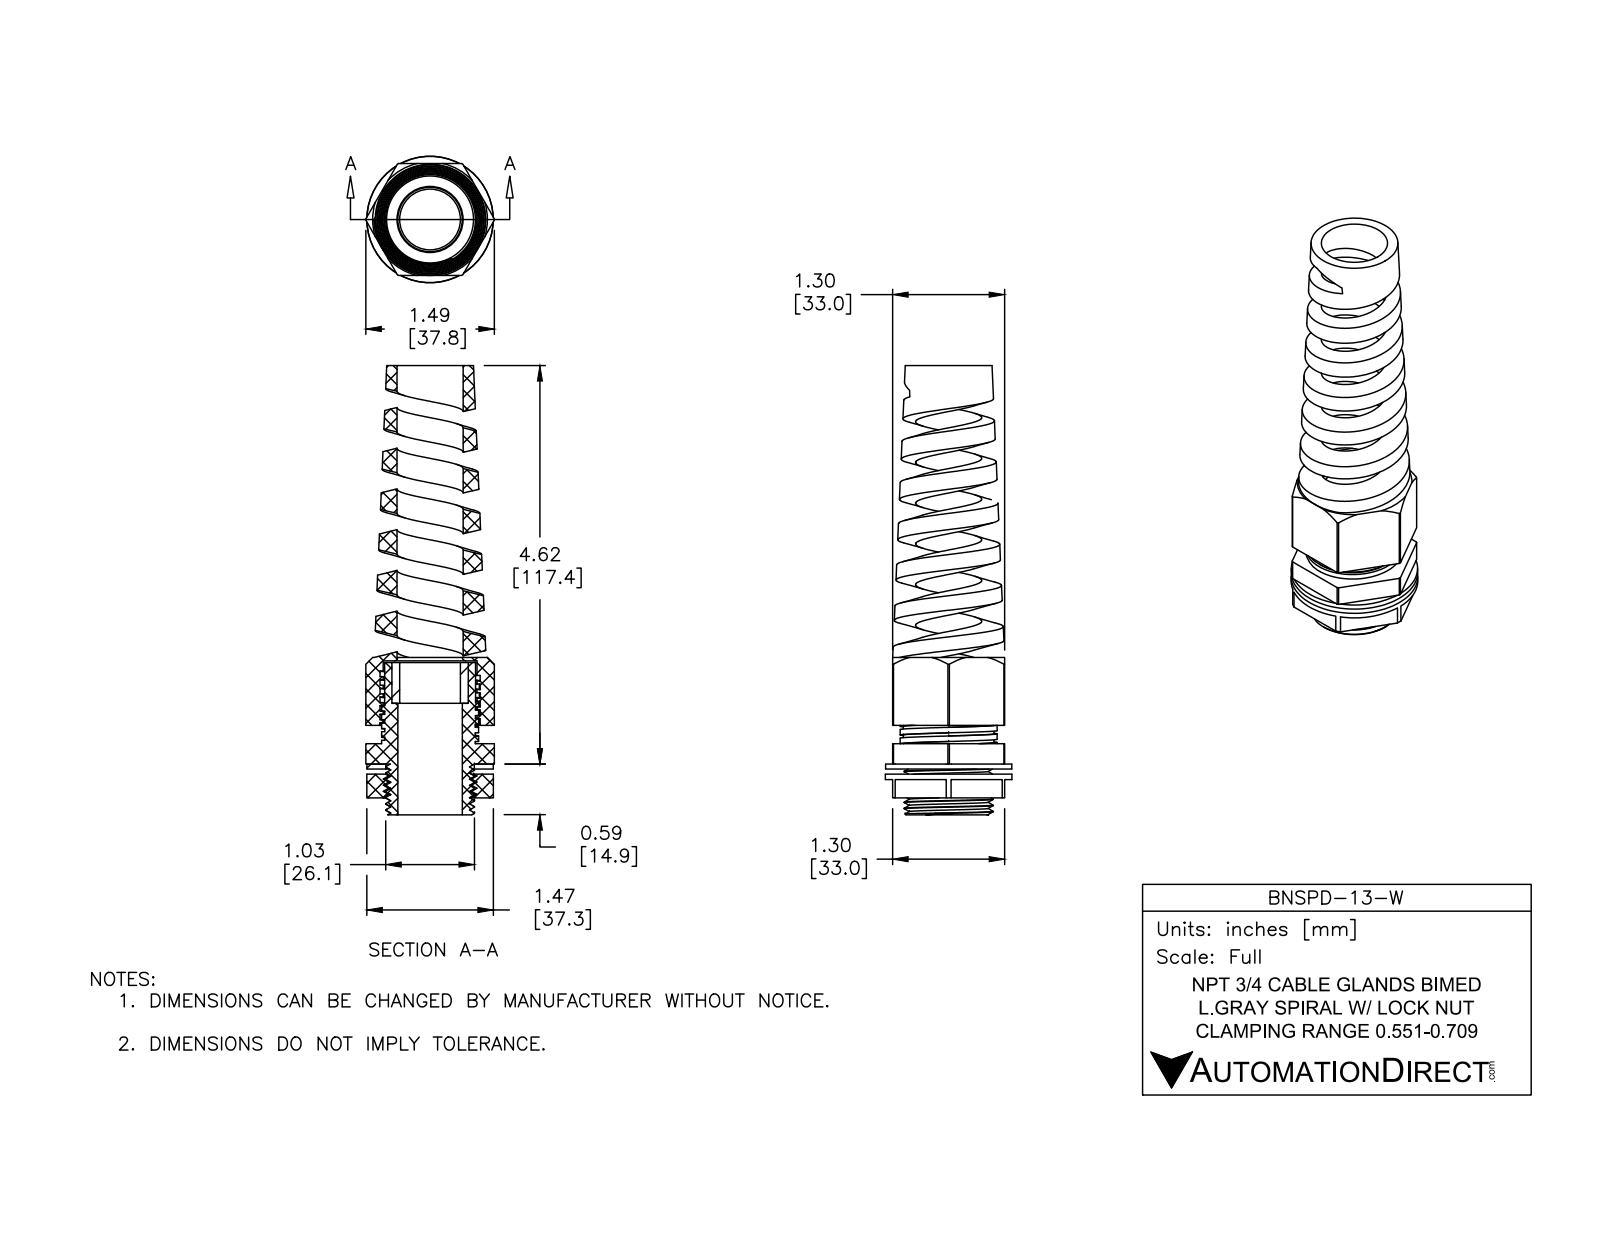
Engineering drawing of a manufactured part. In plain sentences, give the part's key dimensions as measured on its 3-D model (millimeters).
The part is named "BNSPDX-13-W". Its 3-D file was written by "SolidWorks 2015 (CONFIG_CONTROL_DESIGN)". It is 5 solids with 238 faces: 105 planar, 96 cylindrical and 37 other. Overall it measures 132.38 by 37.85 by 37.3 millimeters. Its volume is 41 282 cubic millimeters and its surface area 35 007 square millimeters. Round holes: 1 of diameter 17.9, 1 of diameter 19, 1 of diameter 19.5, 1 of diameter 22.5, 1 of diameter 24.69, 1 of diameter 26.1, 1 of diameter 27.67. Round bosses or shafts: 1 of diameter 37.3, 1 of diameter 37.2, 1 of diameter 28.6, 1 of diameter 26.8, 1 of diameter 26.14. Partial cylindrical surfaces (rounded edges, fillets, slot ends): 1 of radius 18.92. The main face-to-face distances are 33, 1.5, 32.9, 31.4, 3, 0.5, 16, 5.4, 7, 8.5.
